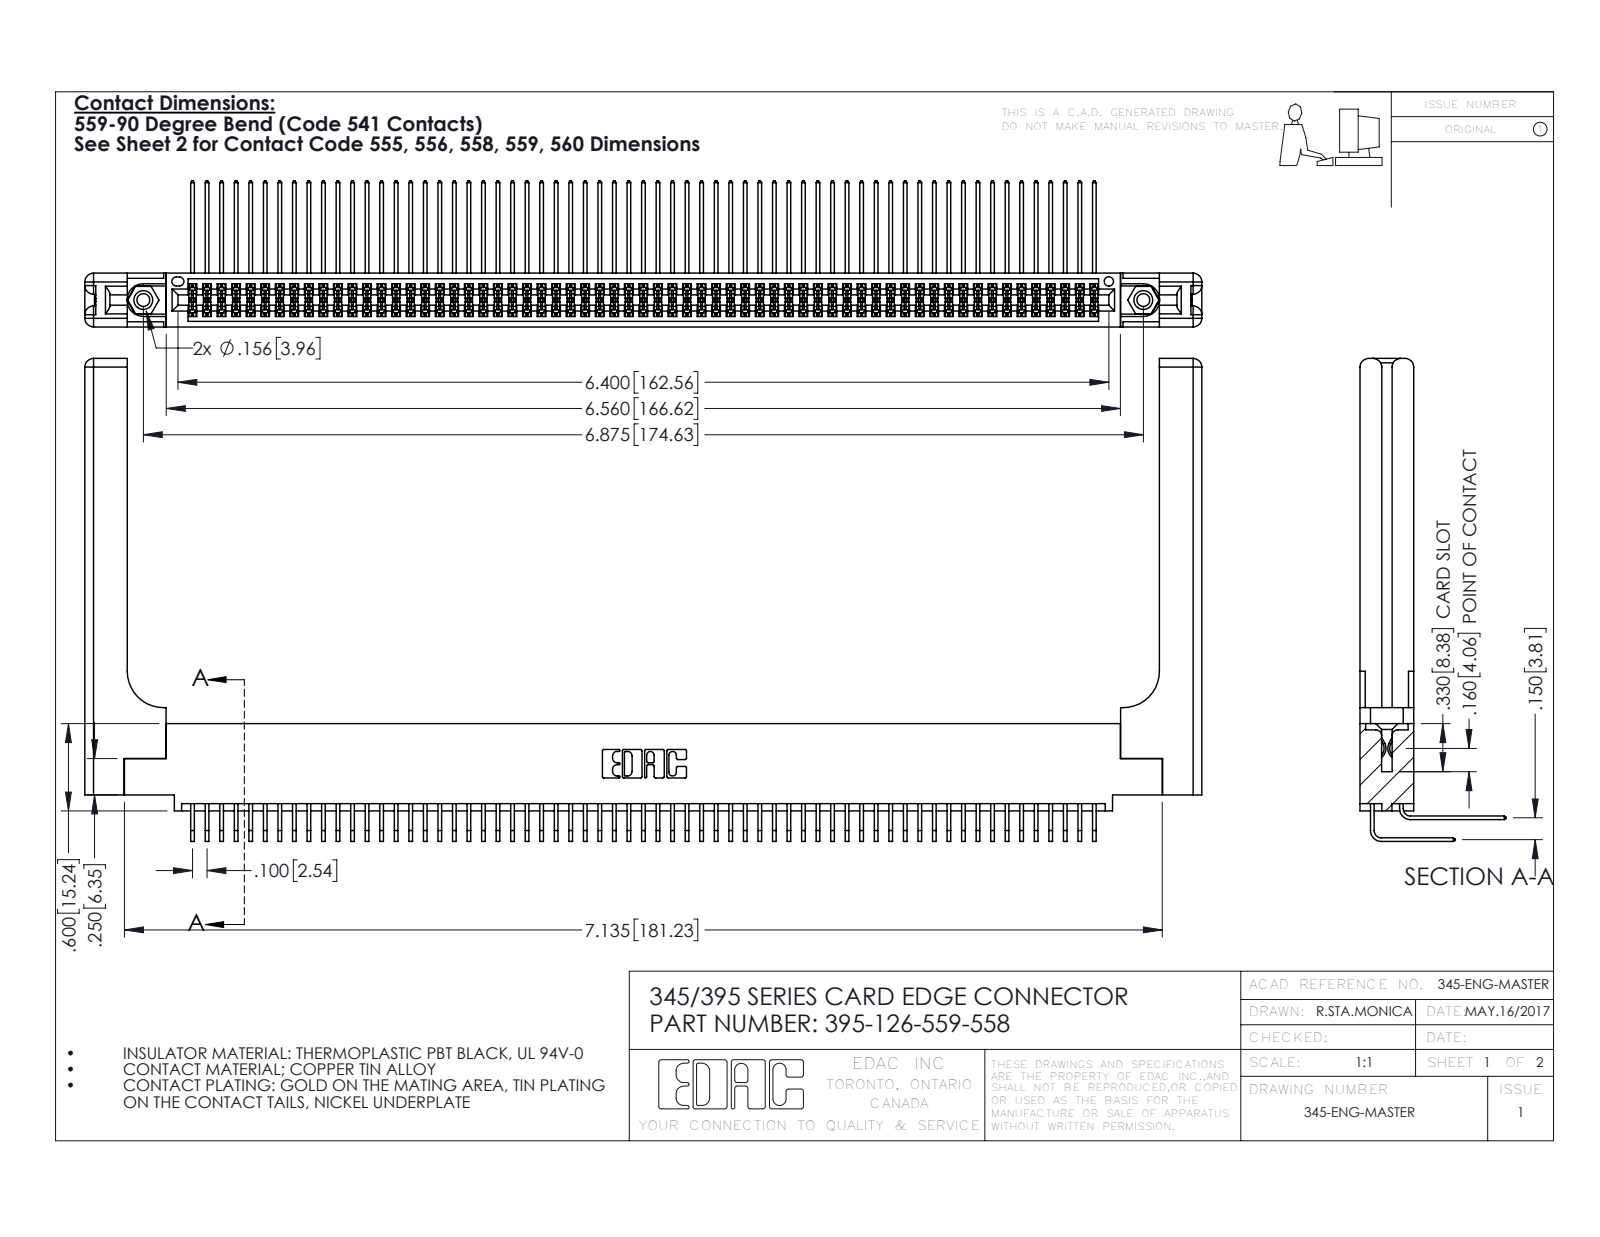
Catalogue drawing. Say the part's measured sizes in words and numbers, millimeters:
The part is named "345-250-001_345-250-001-102; 345-292-001_558 559 Tail - 1; 345 Part_0.110 Offset - 0.156 Dia-TH; 345-292-001_559 Tail - 2 (+2 more)". Its 3-D file was written by "SolidWorks 2016 (CONFIG_CONTROL_DESIGN)". It is 131 solids with 6938 faces: 4642 planar, 2236 cylindrical and 60 other. Overall it measures 195 by 84.3 by 25.5 millimeters. Its volume is 28 270 cubic millimeters and its surface area 38 240 square millimeters. Round holes: 2 of diameter 2.3, 2 of diameter 3.2, 2 of diameter 4, 1 of diameter 1.6. Round bosses or shafts: 2 of diameter 3.9. Partial cylindrical surfaces (rounded edges, fillets, slot ends): 190 of radius 0.2, 22 of radius 0.3, 16 of radius 1.5, 6 of radius 0.2, 6 of radius 0.8, 3 of radius 0.7, 2 of radius 0.4, 2 of radius 0.5. The main face-to-face distances are 1.8, 7.6, 9.4, 2.5, 6.9, 0.6, 5.1, 5.7, 4.4, 3.8. The hole center spacings are 6.9, 168.6, 174.6.
